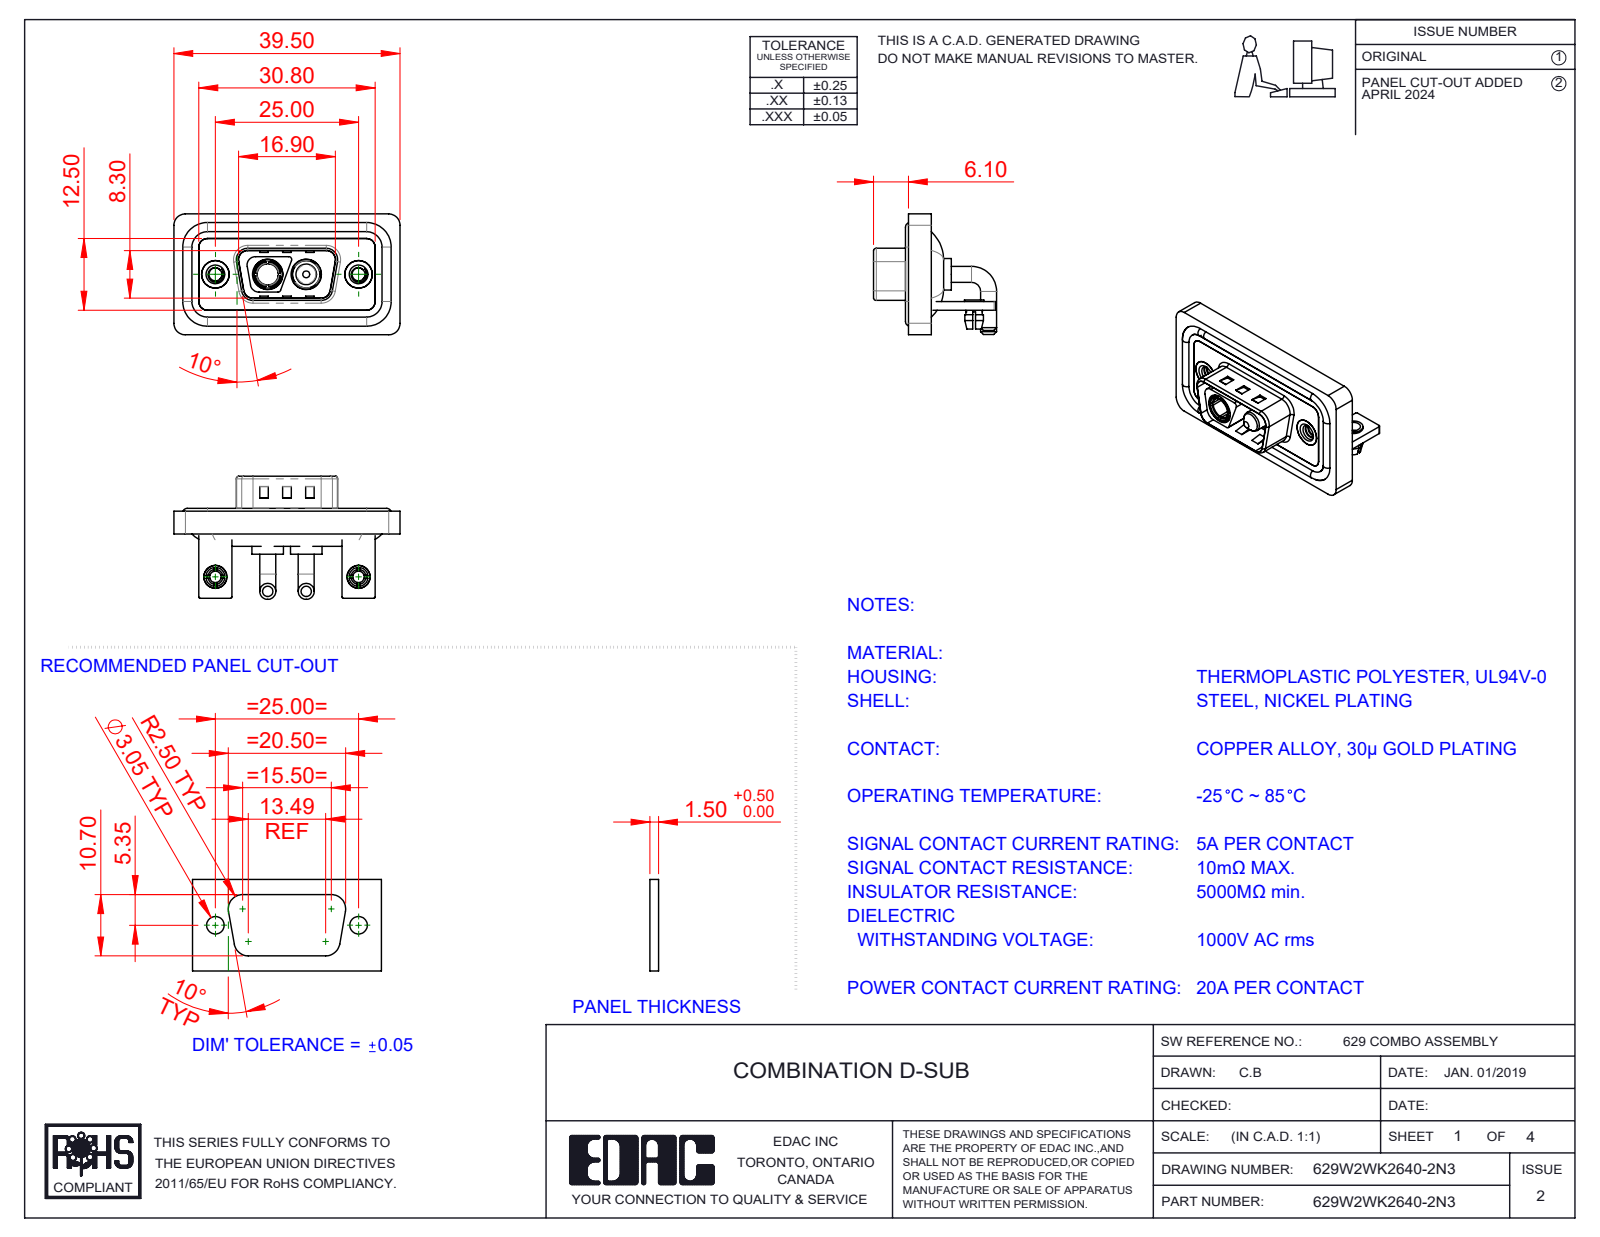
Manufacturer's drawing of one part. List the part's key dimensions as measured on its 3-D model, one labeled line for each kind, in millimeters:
Part name (STEP PRODUCT): Power Socket_20A RA; 629Combo Threaded Rivet_3; Power Pin_20A RA; 629Combo Housing_2WK2 (+6 more)
STEP written by: SolidWorks 2023 (CONFIG_CONTROL_DESIGN)
Units: millimetres
Bodies: 15 solids, 674 faces (257 planar, 281 cylindrical, 136 other)
Overall size (bounding box): 39.5 × 21.5 × 21.1
Volume: 4 996 mm³ · Surface area: 8 329 mm²
Round holes (diameter × count): ⌀2 ×2, ⌀2.26 ×2, ⌀2.5 ×2, ⌀3.2 ×2, ⌀4 ×2, ⌀4.8 ×2, ⌀4.85 ×2, ⌀5 ×2, ⌀5.3 ×2, ⌀3.7 ×1
Round bosses / shafts (diameter × count): ⌀2.8 ×4, ⌀1.6 ×4, ⌀5.5 ×2, ⌀5.2 ×2, ⌀4.9 ×2, ⌀4.75 ×2, ⌀4 ×2, ⌀3.75 ×2
Partial cylindrical surfaces — rounded edges, fillets, slot ends (radius × count): R1.5 ×20, R2 ×19, R0.25 ×16, R0.5 ×11, R1.6 ×8, R0.6 ×4, R0.65 ×4, R0.9 ×4
Main face-to-face distances: 0.4, 1.5, 2.9, 0.8, 1.1, 1.2, 2.1, 1.6, 3.7, 2.5
Hole centre spacings: 9.14, 15.86, 25, 6.72
